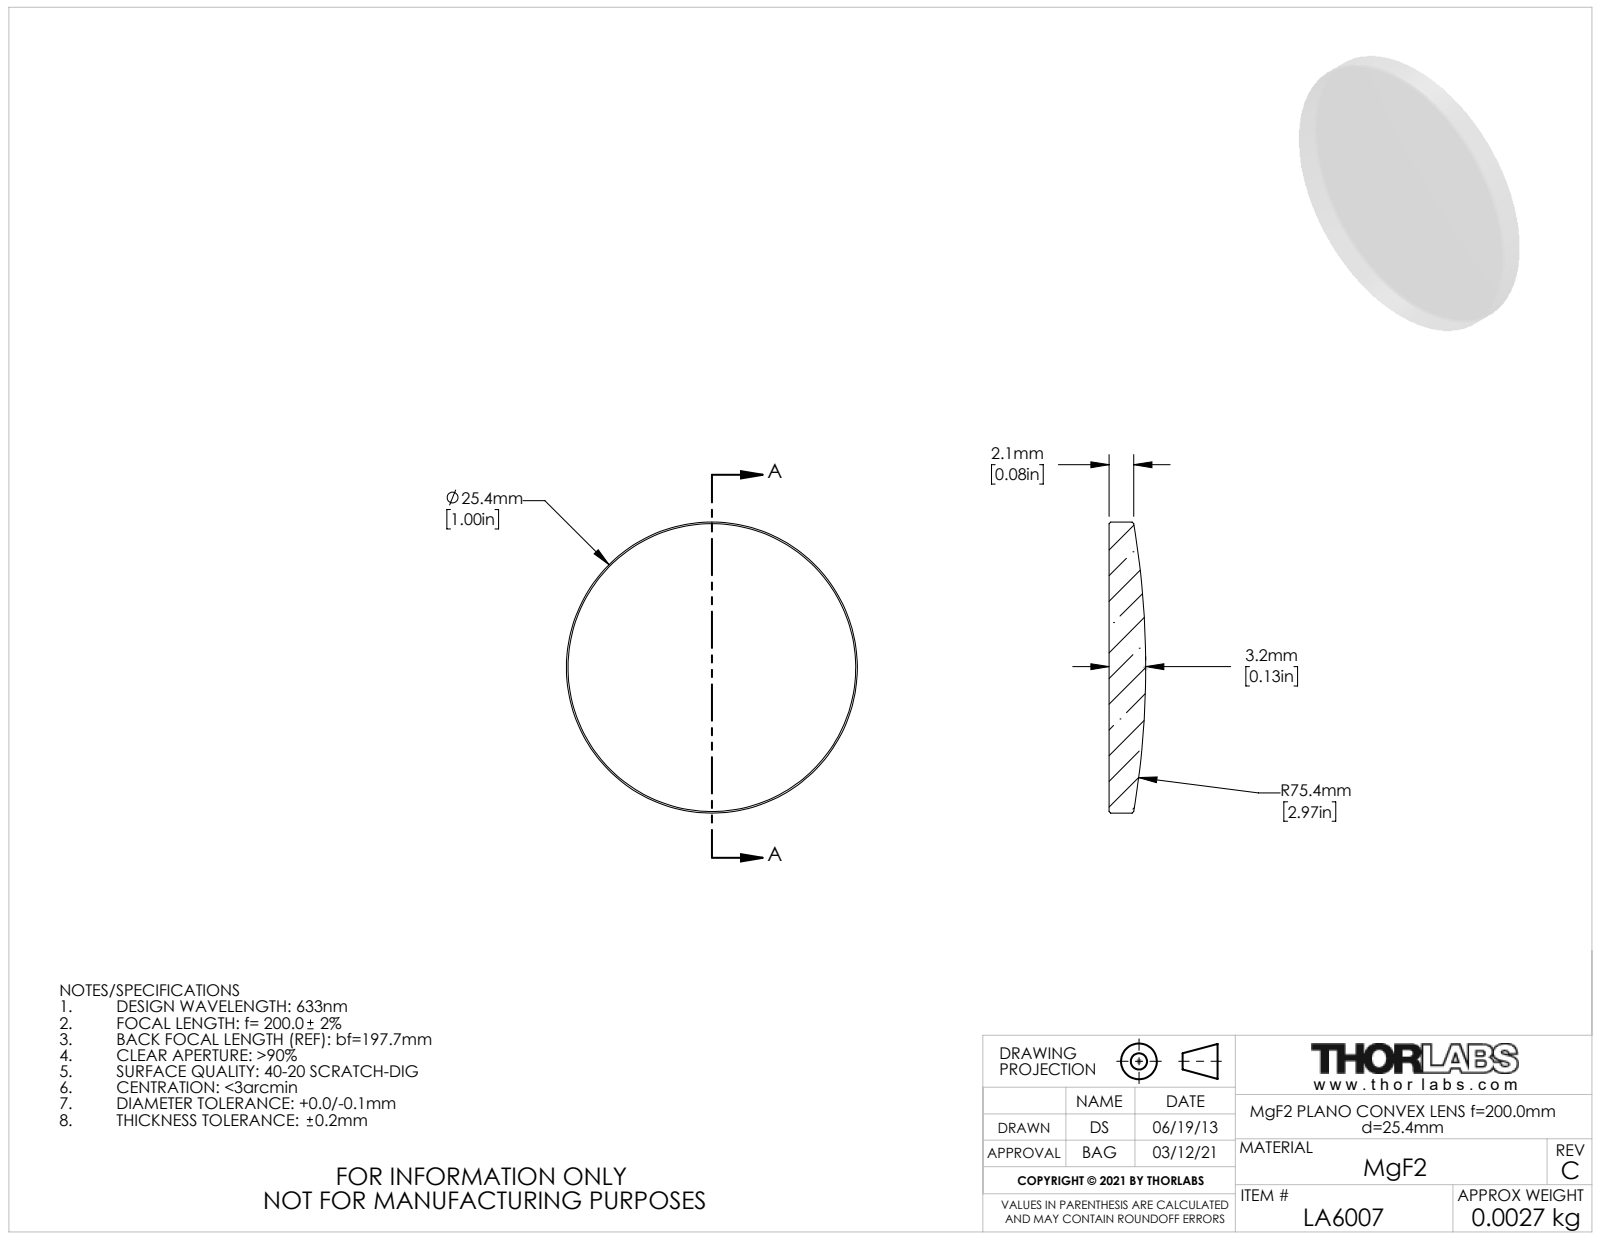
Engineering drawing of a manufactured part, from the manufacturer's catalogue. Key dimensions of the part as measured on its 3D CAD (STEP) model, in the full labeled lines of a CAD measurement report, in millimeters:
Part name (STEP PRODUCT): 7258-E0W
STEP written by: SolidWorks 2007 (AUTOMOTIVE_DESIGN)
Units: millimetres
Bodies: 0 solids, 5 faces (1 planar, 2 cylindrical, 2 other)
Overall size (bounding box): 25.4 × 25.4 × 2.6
Round bosses / shafts (diameter × count): ⌀25.4 ×1
